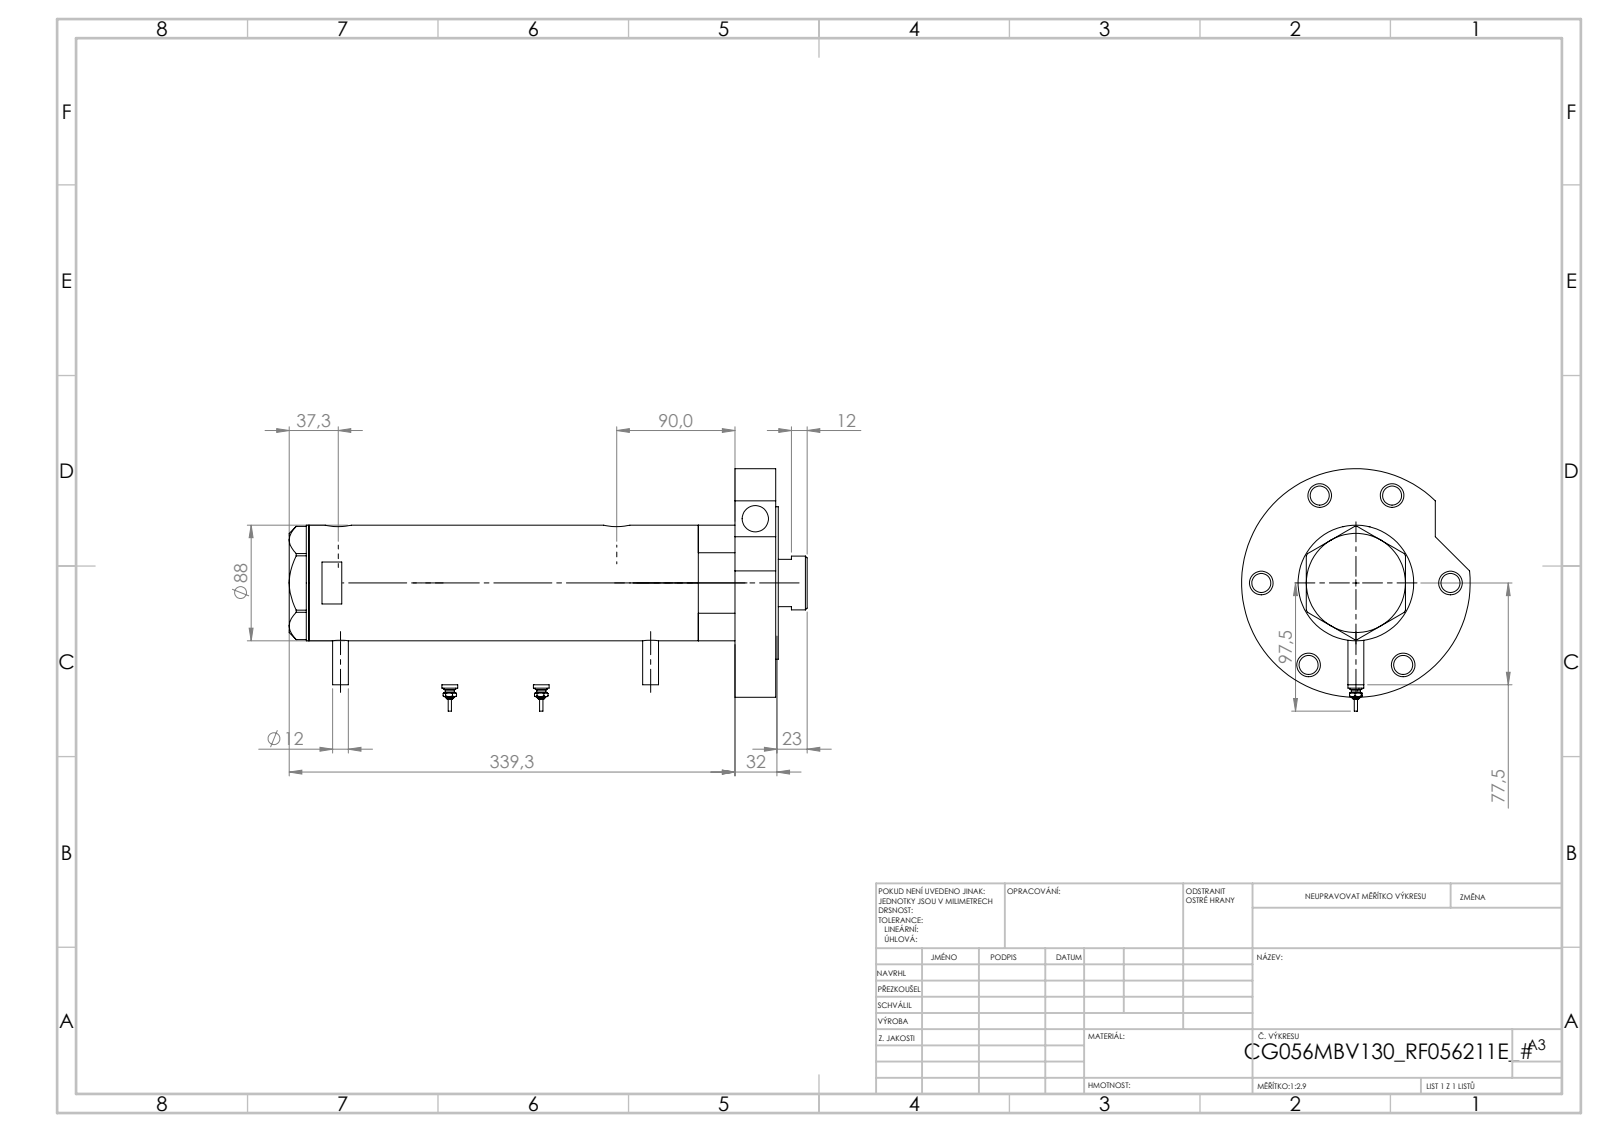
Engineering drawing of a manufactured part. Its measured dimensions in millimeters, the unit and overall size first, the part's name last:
Units: millimetres
Overall size (bounding box): 394.3 × 184.5 × 174
Round holes (diameter × count): ⌀14.5 ×7, ⌀18 ×6, ⌀20 ×3, ⌀12.5 ×2, ⌀13.16 ×2, ⌀42 ×1, ⌀43.5 ×1, ⌀56 ×1, ⌀60 ×1, ⌀75 ×1, ⌀80 ×1
Round bosses / shafts (diameter × count): ⌀12 ×4, ⌀9 ×2, ⌀7 ×2, ⌀4.5 ×2, ⌀2.5 ×2, ⌀174 ×1, ⌀116 ×1, ⌀88 ×1
Main face-to-face distances: 31, 2, 357.3, 324.3, 355.3, 33, 234.4, 89.9, 120.9, 122.9
Hole centre spacings: 72, 80, 119.73, 124.71, 129.15, 143.69, 1.7, 25.8
Volume: 2 582 000 mm³ · Surface area: 361 571 mm²
Bodies: 7 solids, 257 faces (91 planar, 102 cylindrical, 64 other)
Part name (STEP PRODUCT): V270CG_RF211E; V270CG_MIDDLE; V270CG_VC; V270CG_BACK (+2 more)
STEP written by: SolidWorks 2019 (CONFIG_CONTROL_DESIGN)
